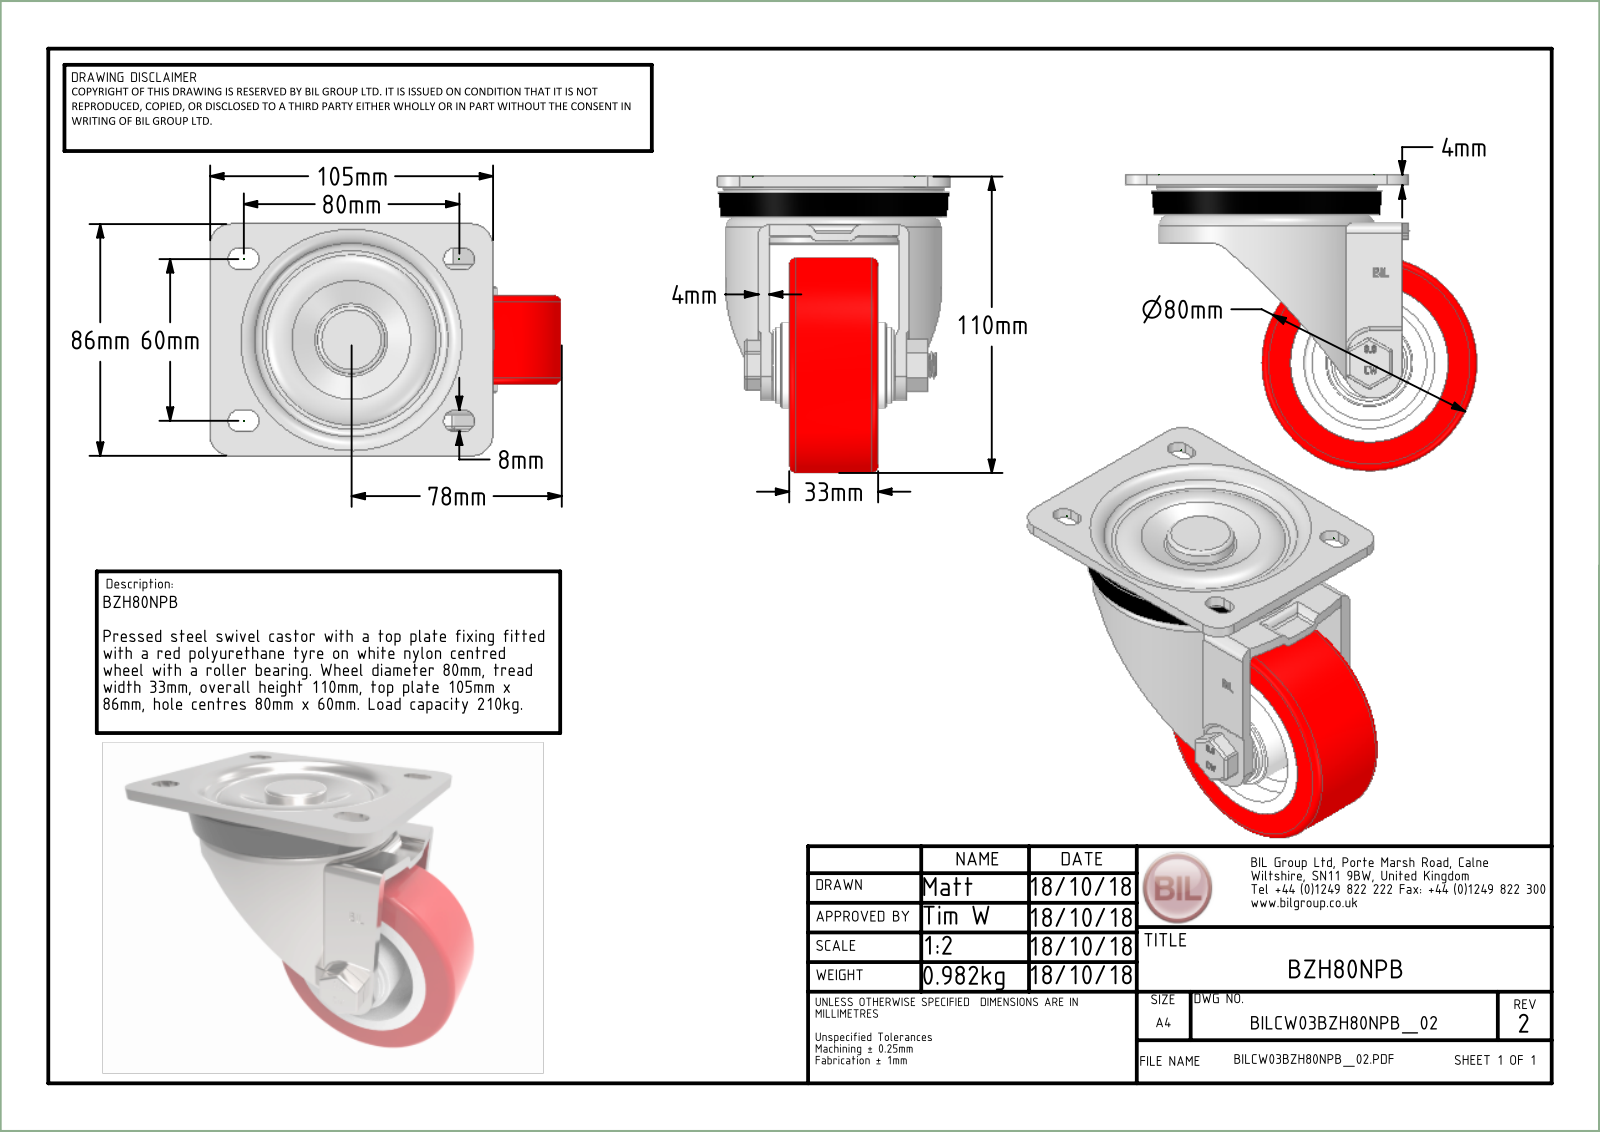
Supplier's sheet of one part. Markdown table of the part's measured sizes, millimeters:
| quantity | value |
| --- | --- |
| part name | BZH80NPB v4; BZH80AS - 2 v2; ZINC PLATED, PRESSED STEEL TOP PLATE; ZINC PLATED, PRESSED STEEL FORKS (+8 more) |
| STEP written by | Autodesk Translation Framework v14.10.0.0 (AUTOMOTIVE_DESIGN) |
| units | millimeters |
| bodies | 19 solids, 483 faces (240 planar, 147 cylindrical, 96 other) |
| overall size | 130.5 × 110 × 86 |
| volume | 268 992 mm³ |
| surface area | 115 007 mm² |
| round holes (diameter × count) | 10 × 1, 10.2 × 1, 12 × 1, 12.5 × 1, 13 × 1, 20.8 × 1, 22.5 × 1, 25 × 1, 32 × 1, 59 × 1, 72 × 1 |
| round bosses / shafts (diameter × count) | 3.75 × 8, 80 × 1, 50.5 × 1, 31 × 1, 26.25 × 1, 22.3 × 1, 20 × 1, 19.5 × 1 |
| partial cylindrical surfaces (radius × count) | 0.5 × 18, 4.5 × 8, 0.75 × 6, 2 × 4, 8 × 4, 4 × 2, 24.49 × 2, 13.13 × 1 |
| main face-to-face distances | 4, 7.5, 10.5, 11.5, 6.5, 16, 3, 39.5, 50, 43.5 |
